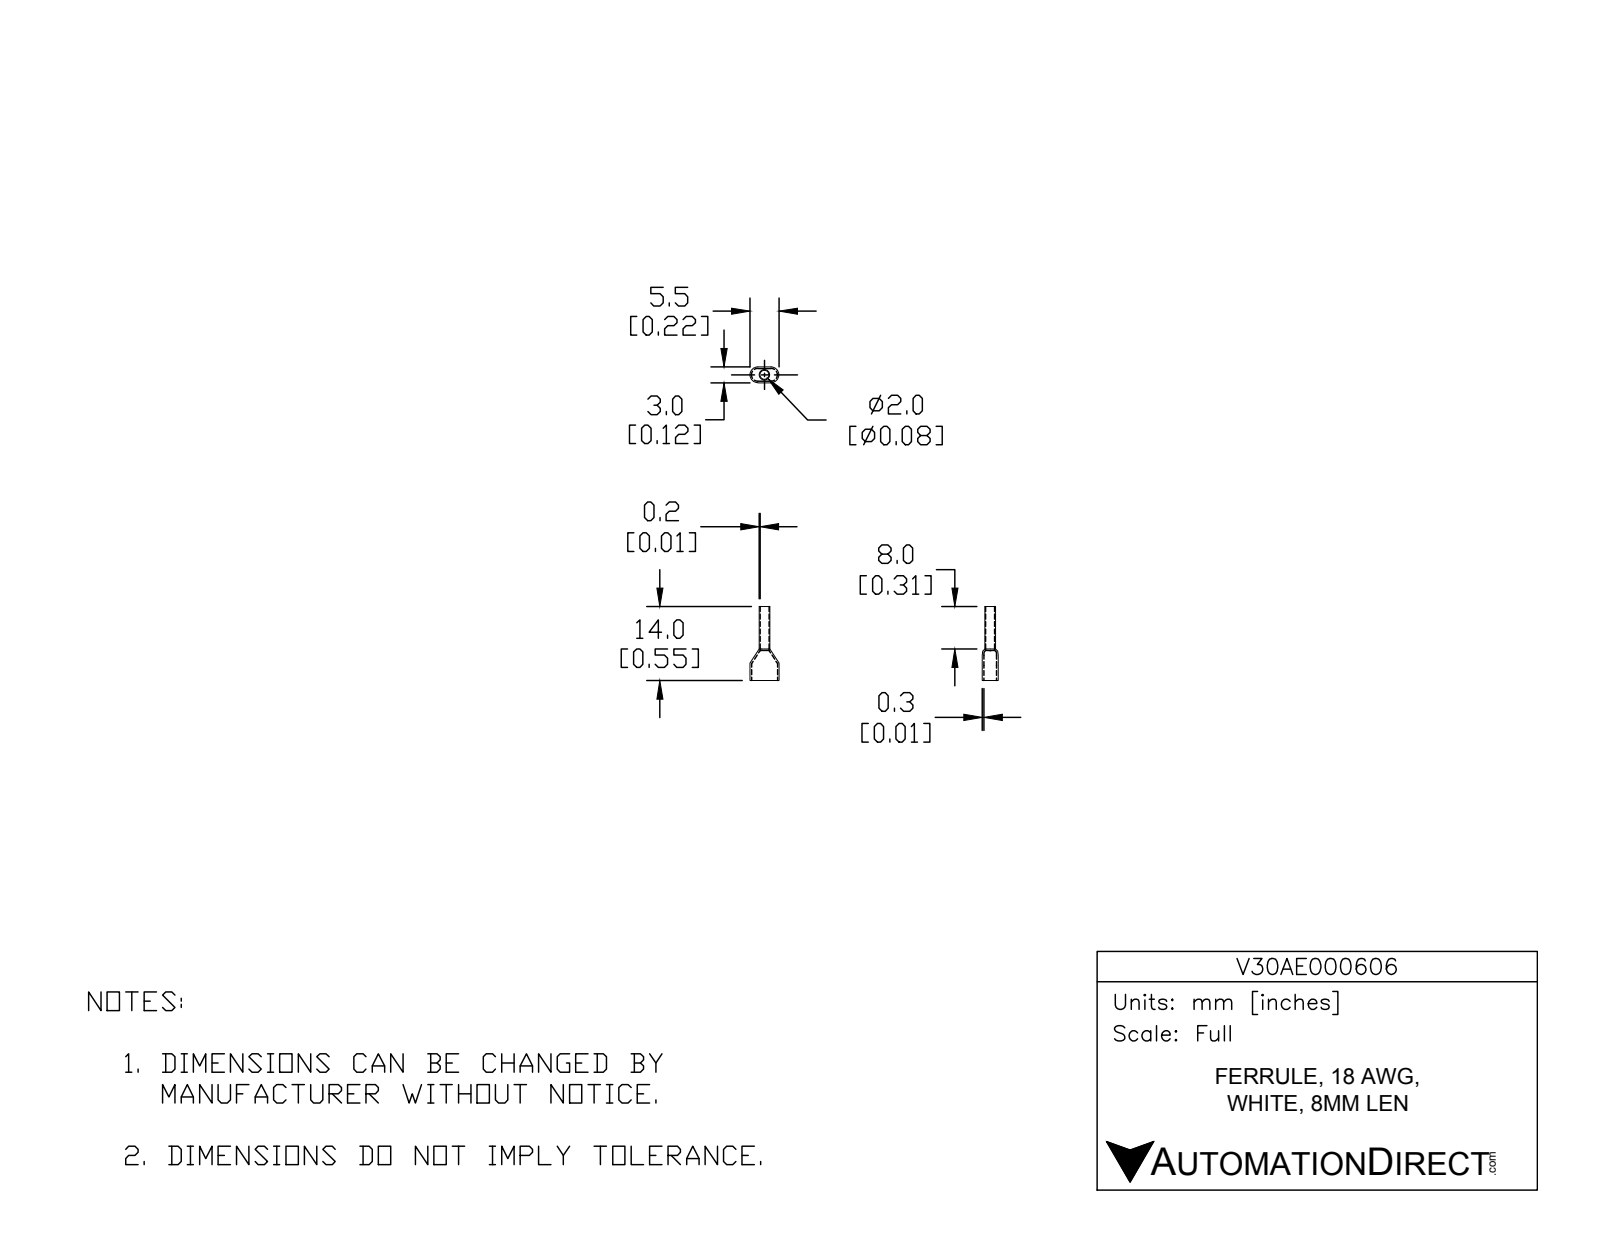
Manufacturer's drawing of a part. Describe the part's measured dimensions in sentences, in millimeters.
The part is named "V30AE000606". Its 3-D file was written by "SolidWorks 2017 (AUTOMOTIVE_DESIGN)". It is 2 solids with 36 faces: 14 planar, 22 cylindrical and 0 other. Overall it measures 14 by 5.5 by 3 millimeters. Its volume is 29 cubic millimeters and its surface area 246 square millimeters. Round holes: 1 of diameter 1.7. Round bosses or shafts: 1 of diameter 2. Partial cylindrical surfaces (rounded edges, fillets, slot ends): 4 of radius 1.2, 4 of radius 1.5. The main face-to-face distances are 2.7, 3, 2.4, 6, 14, 8, 5.7, 8.3.
